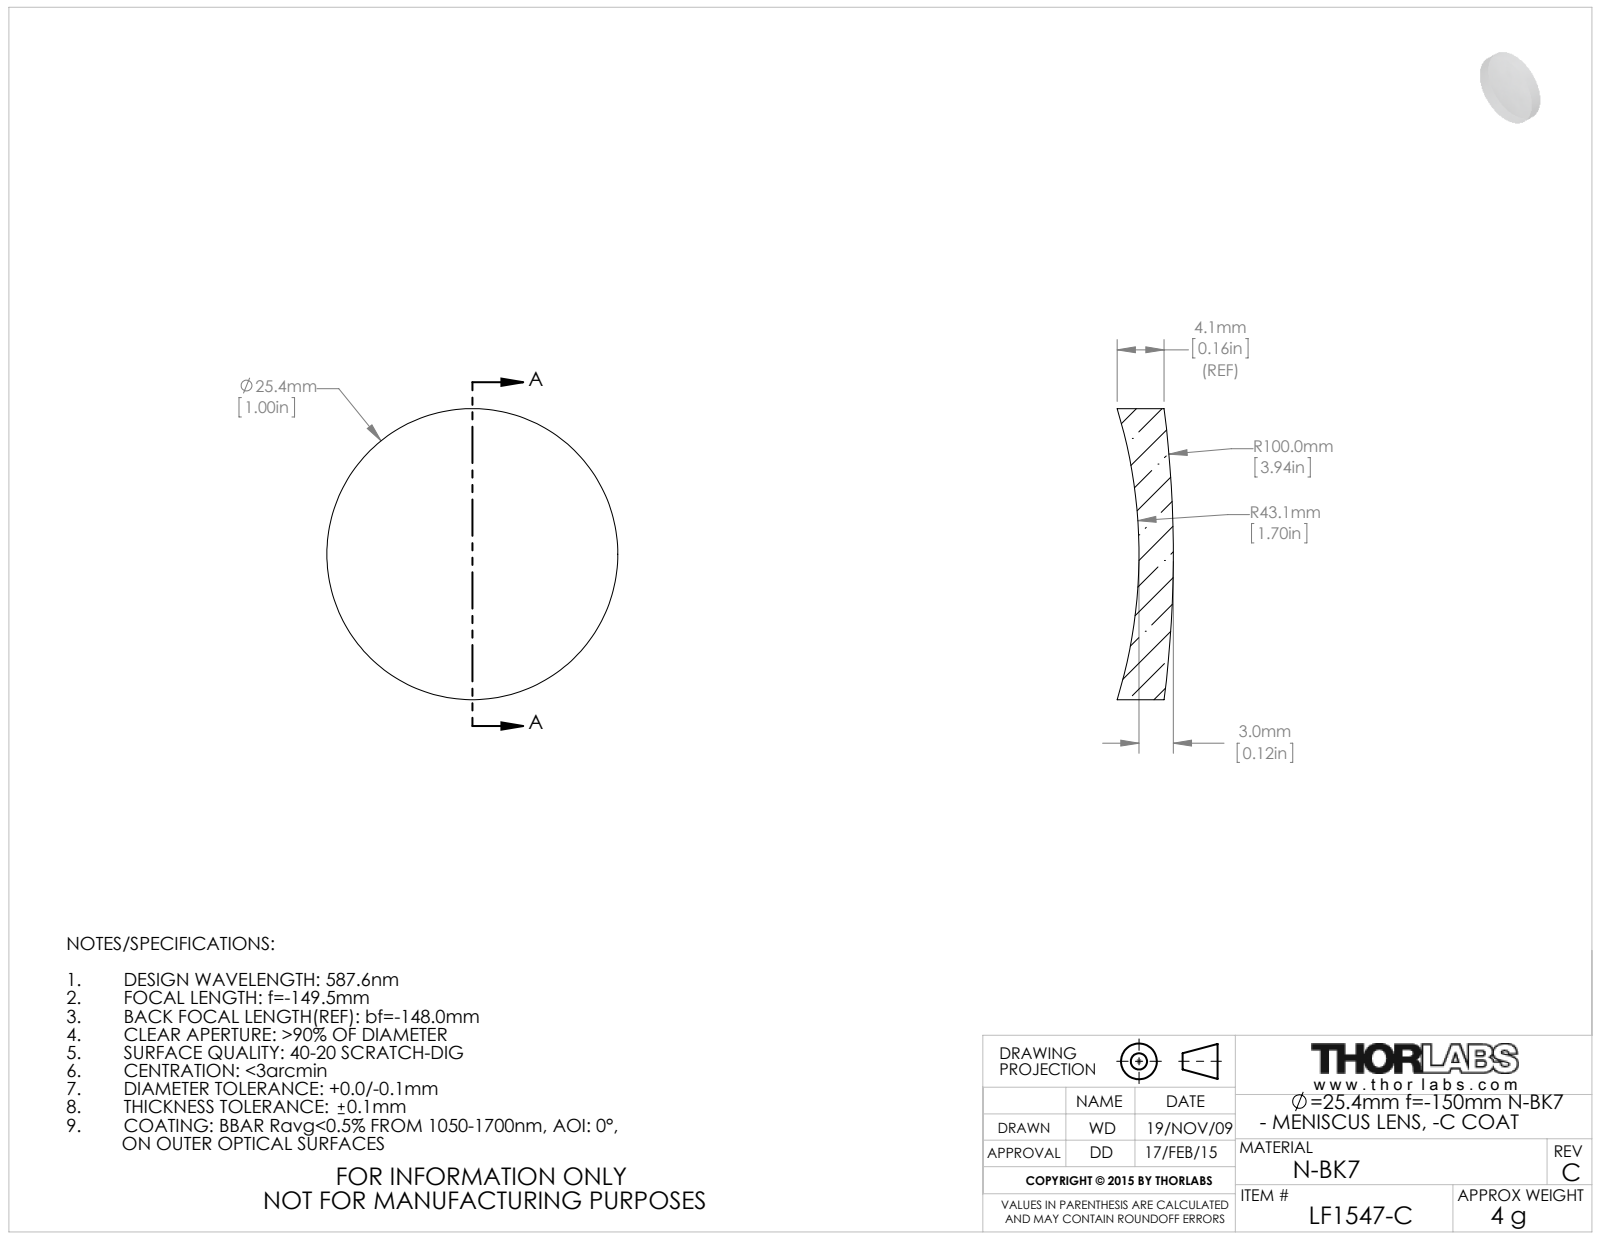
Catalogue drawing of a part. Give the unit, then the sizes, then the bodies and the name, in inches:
Units: inches
Overall size (bounding box): 1 × 1 × 0.193
Round bosses / shafts (diameter × count): ⌀1 ×1
Volume: 0.11 in³ · Surface area: 2.099 in²
Bodies: 1 solid, 6 faces (0 planar, 2 cylindrical, 4 other)
Part name (STEP PRODUCT): 4907-E0W
STEP written by: SolidWorks 2009 (AUTOMOTIVE_DESIGN)
